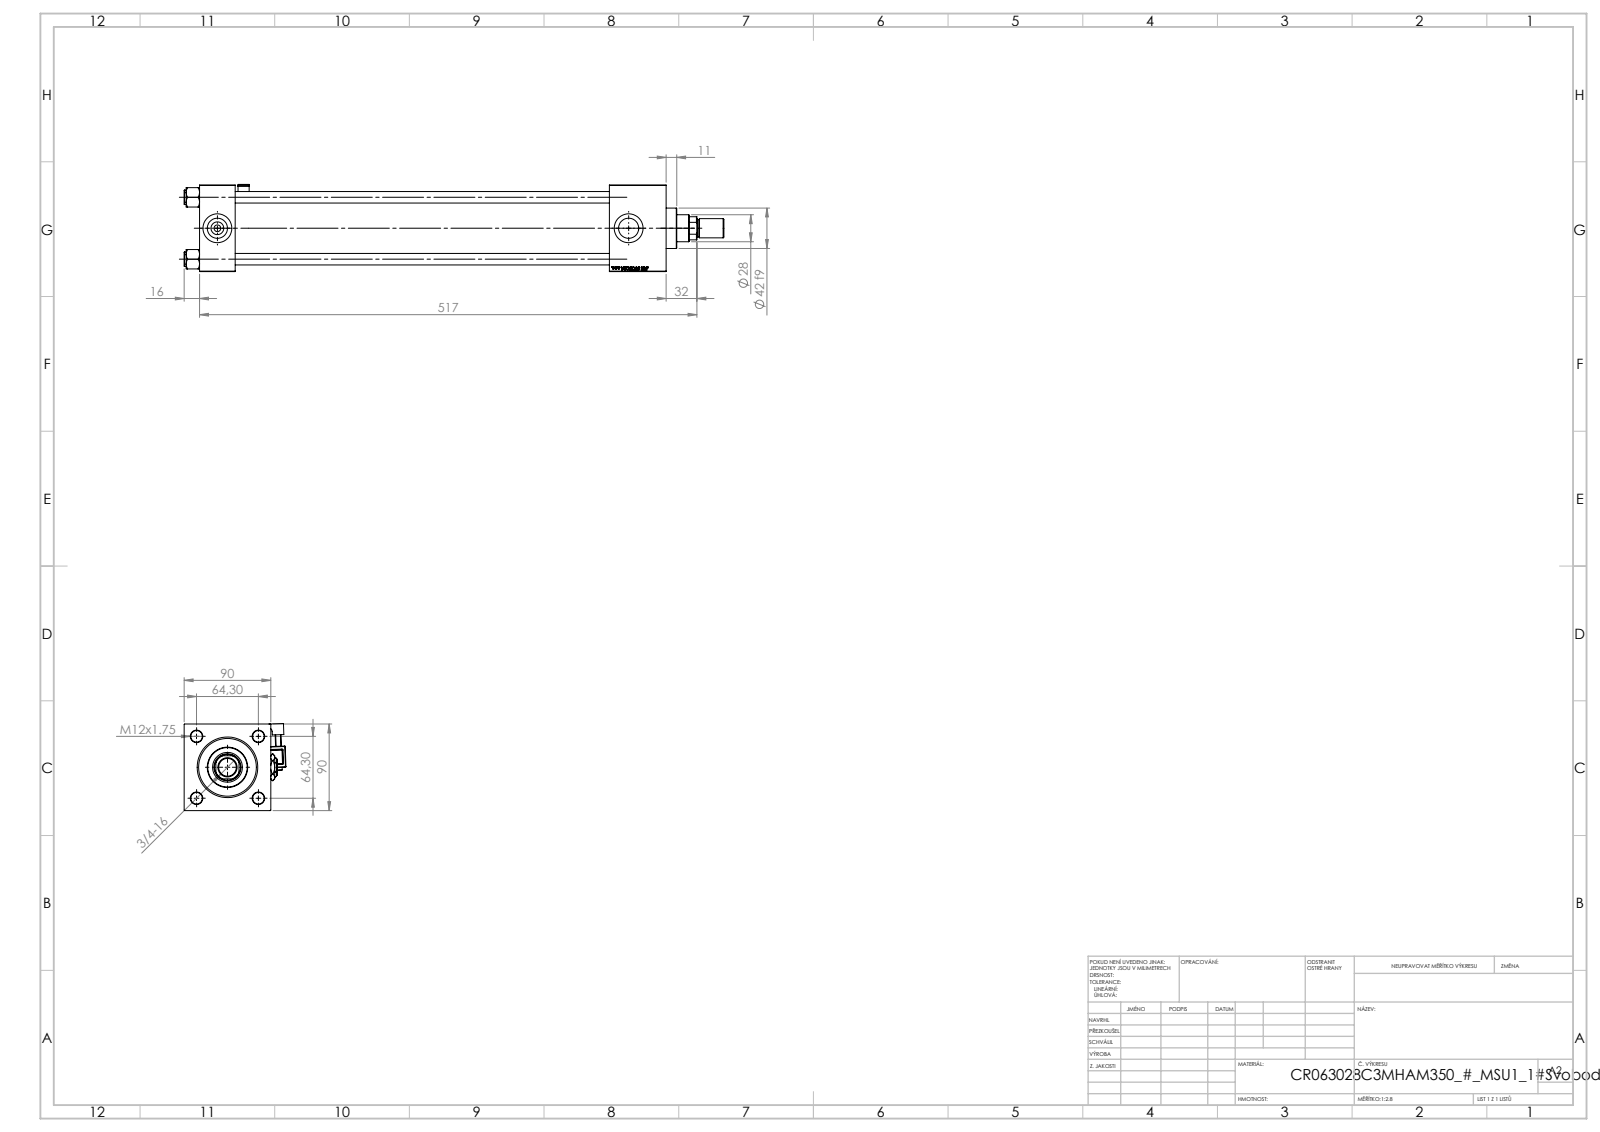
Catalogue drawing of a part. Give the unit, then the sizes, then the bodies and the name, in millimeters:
Units: millimetres
Overall size (bounding box): 561 × 105.78 × 90.53
Round holes (diameter × count): ⌀12 ×4, ⌀7 ×2, ⌀20.96 ×2, ⌀30 ×2, ⌀18.5 ×1, ⌀28 ×1, ⌀31 ×1, ⌀50 ×1, ⌀60 ×1, ⌀63 ×1
Round bosses / shafts (diameter × count): ⌀15 ×4, ⌀69 ×1, ⌀42 ×1, ⌀20 ×1, ⌀18 ×1, ⌀6 ×1
Partial cylindrical surfaces — rounded edges, fillets, slot ends (radius × count): R0.5 ×24, R1 ×1, R2.5 ×1, R4 ×1, R13.5 ×1
Main face-to-face distances: 90, 37, 485, 448, 426, 389, 59, 456.3, 419.3, 30.3
Hole centre spacings: 45.47, 64.3, 90.93, 427.5
Volume: 1 527 000 mm³ · Surface area: 408 122 mm²
Bodies: 15 solids, 1341 faces (607 planar, 132 cylindrical, 602 other)
Part name (STEP PRODUCT): V215_VC_A; ROD_END_AH; Zatka_pro_OIL_PORT; NUT_M5_C (+4 more)
STEP written by: SolidWorks 2019 (CONFIG_CONTROL_DESIGN)
